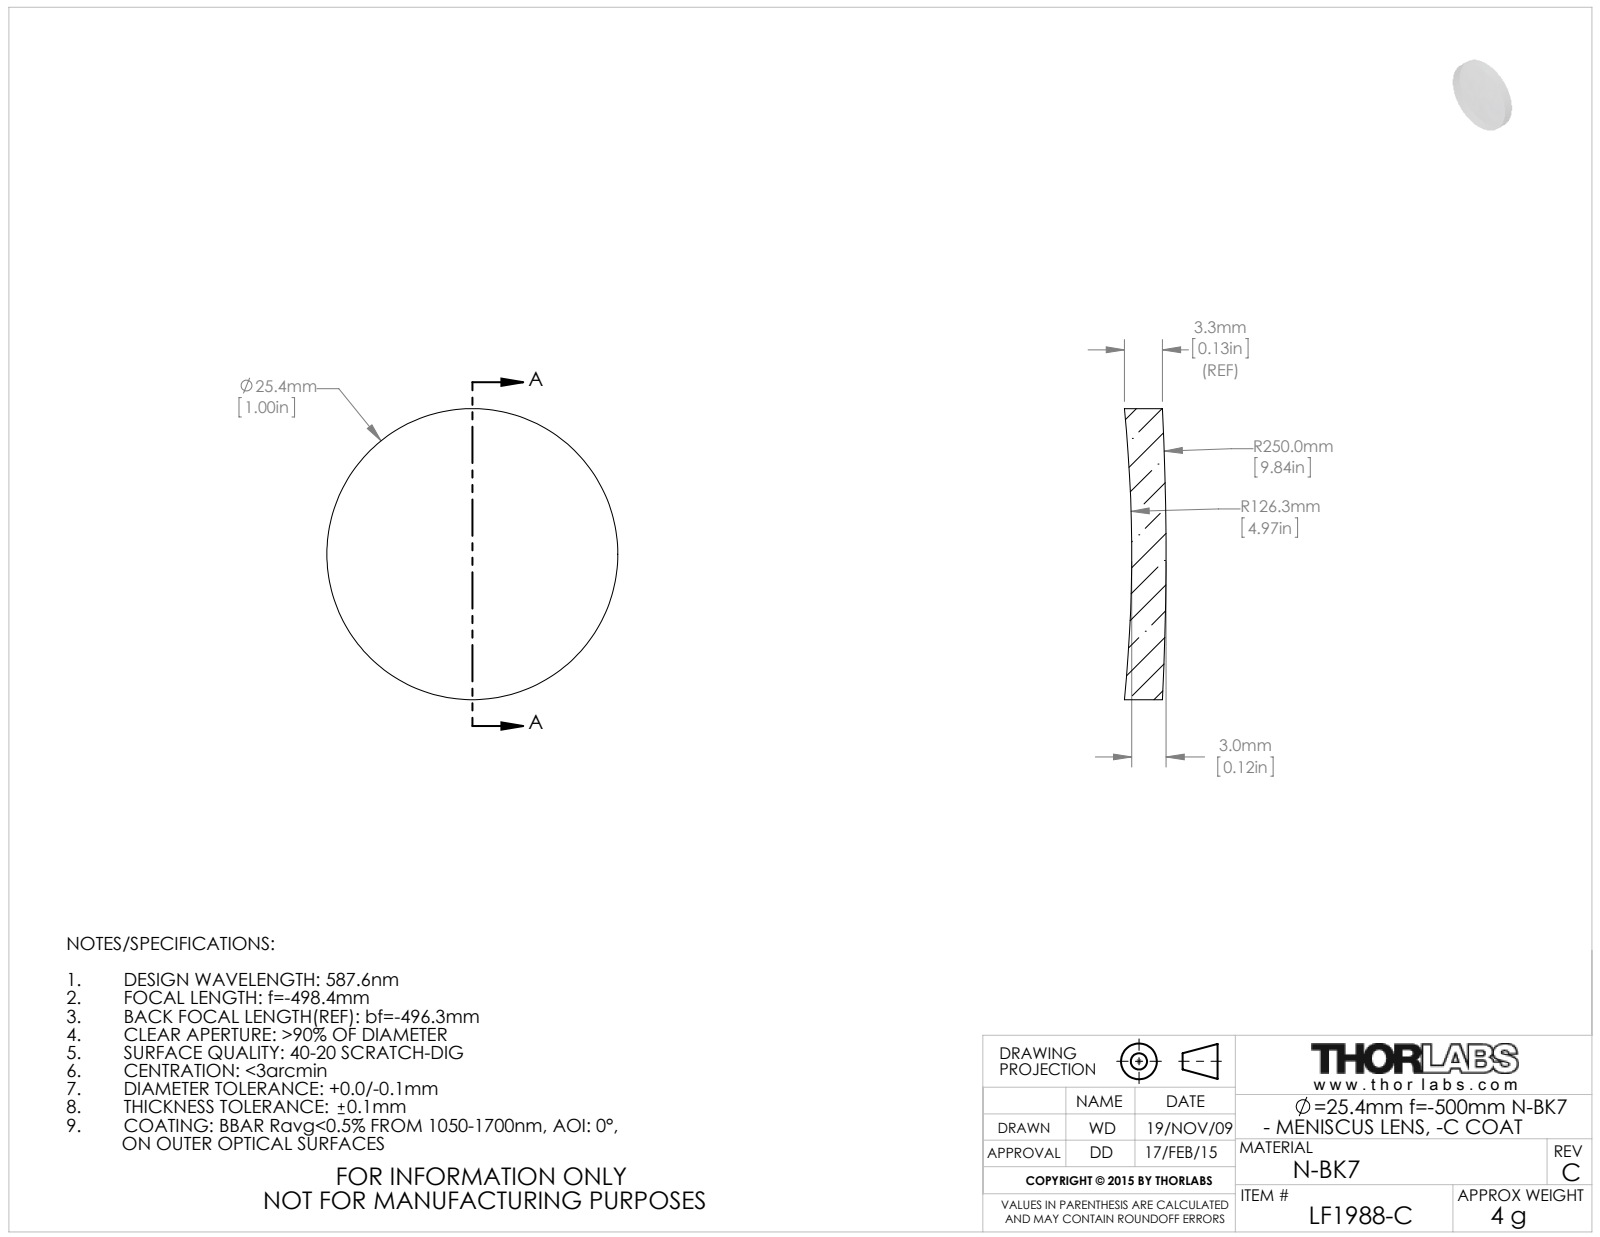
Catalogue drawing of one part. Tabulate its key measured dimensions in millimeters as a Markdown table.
| quantity | value |
| --- | --- |
| part name | 4912-E0W |
| STEP written by | SolidWorks 2009 (AUTOMOTIVE_DESIGN) |
| units | millimeters |
| bodies | 1 solid, 6 faces (0 planar, 2 cylindrical, 4 other) |
| overall size | 25.4 × 25.4 × 3.64 |
| volume | 1 600 mm³ |
| surface area | 1 280 mm² |
| round bosses / shafts (diameter × count) | 25.4 × 1 |
